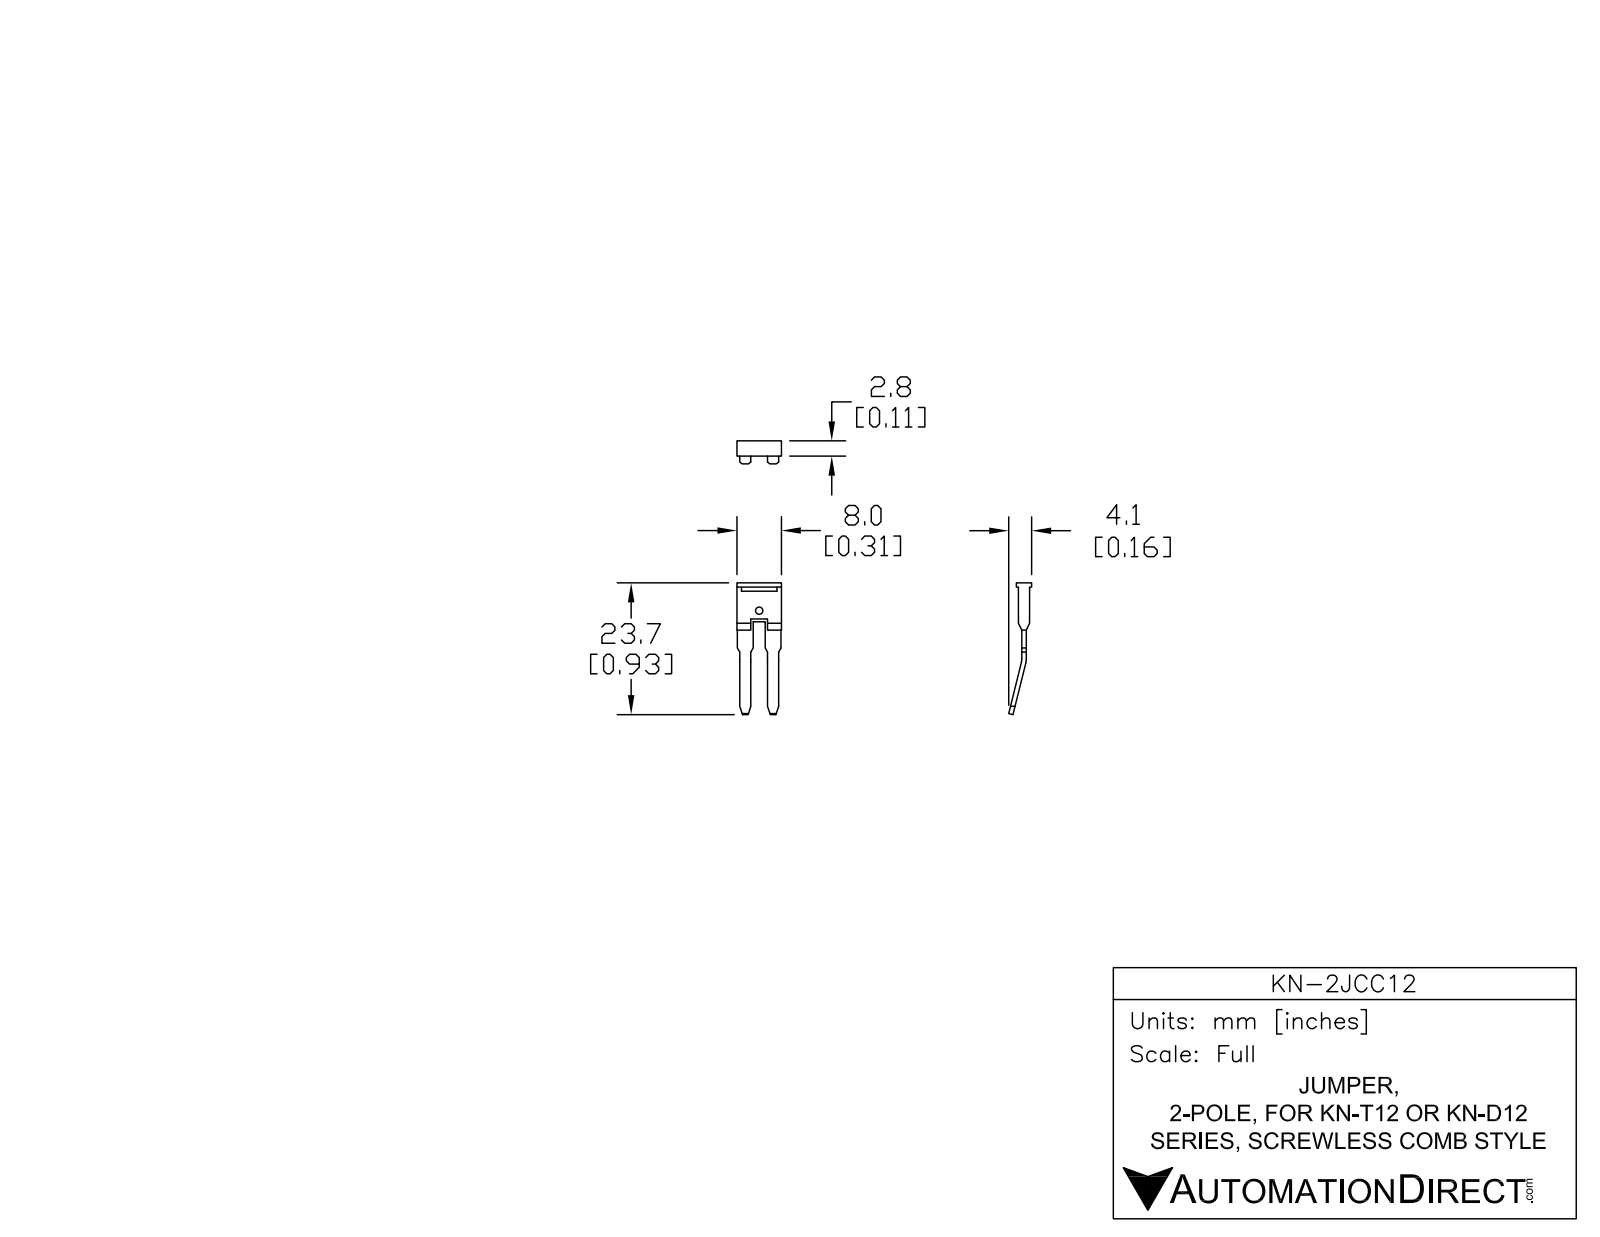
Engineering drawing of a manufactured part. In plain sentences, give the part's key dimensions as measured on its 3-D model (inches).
The part is named "KN-2JCC12". Its 3-D file was written by "SolidWorks 2014 (AUTOMOTIVE_DESIGN)". It is 1 solid with 60 faces: 54 planar, 6 cylindrical and 0 other. Overall it measures 0.933 by 0.315 by 0.163 inches. Its volume is 0.011 cubic inches and its surface area 0.615 square inches. Round holes: 1 of diameter 0.052. Partial cylindrical surfaces (rounded edges, fillets, slot ends): 1 of radius 0.079, 1 of radius 0.11. The main face-to-face distances are 0.031, 0.024, 0.055, 0.079, 0.217, 0.098, 0.02, 0.197, 0.315, 0.295.
